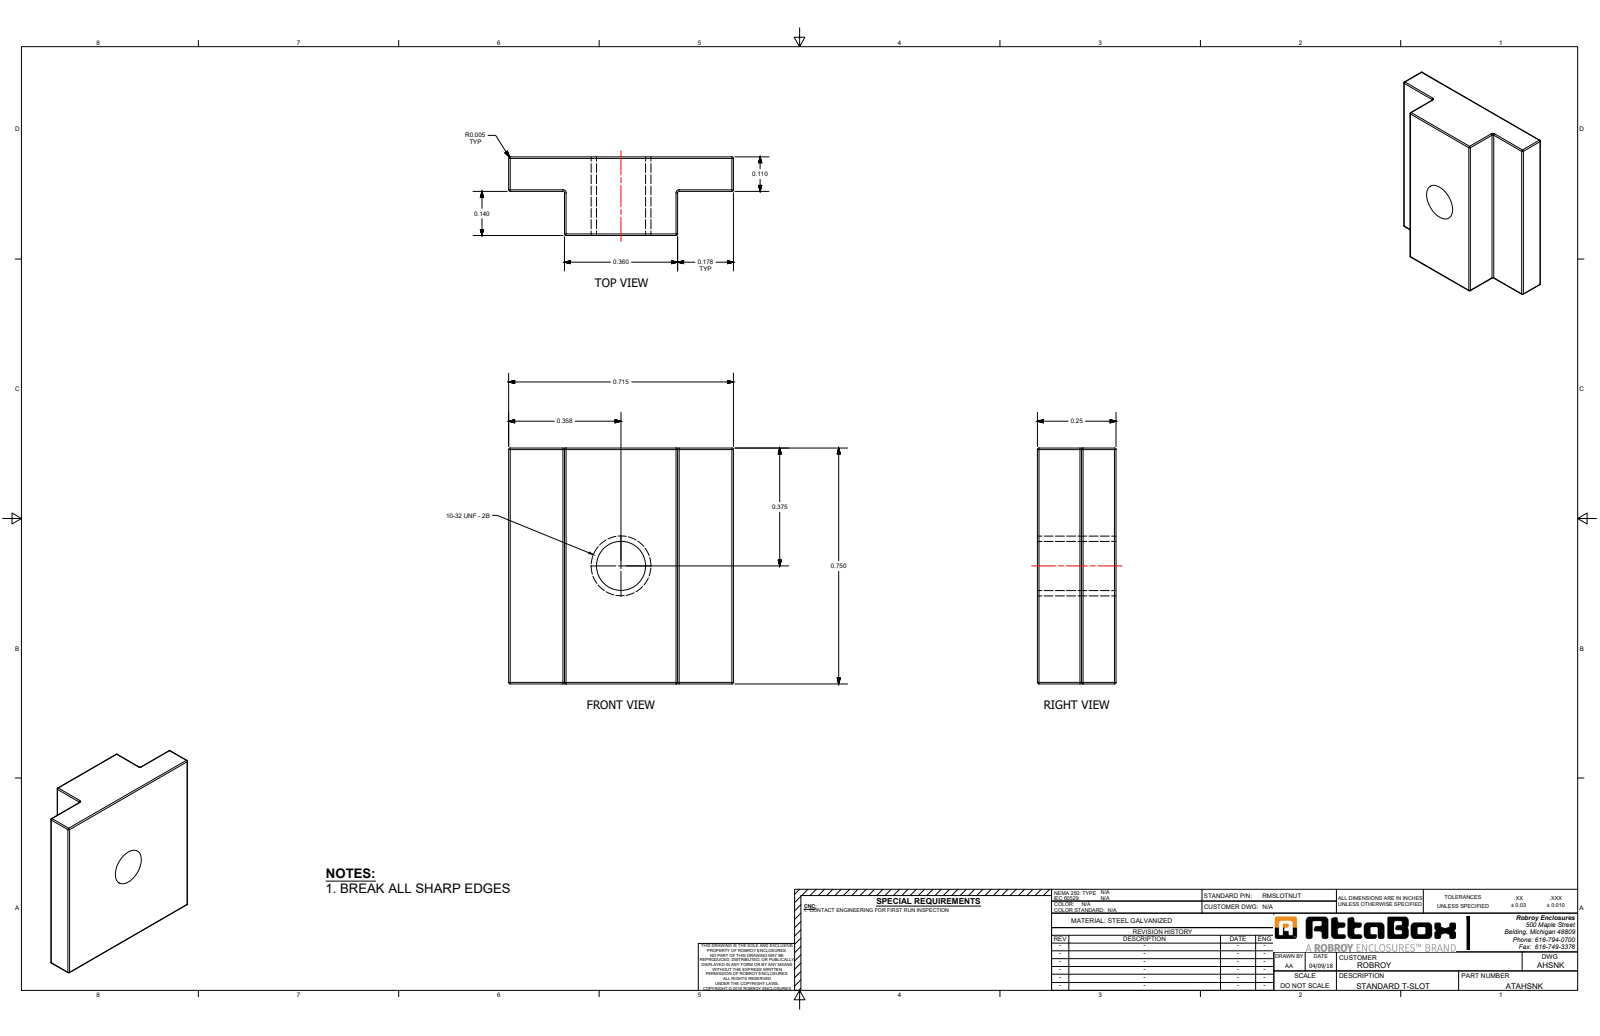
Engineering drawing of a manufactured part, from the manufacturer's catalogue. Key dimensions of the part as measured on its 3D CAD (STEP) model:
Part name (STEP PRODUCT): ATAHSNK
STEP written by: Autodesk Inventor 2018 (AP242_MANAGED_MODEL_BASED_3D_ENGINEERING_MIM_LF)
Units: inches
Bodies: 1 solid, 51 faces (10 planar, 25 cylindrical, 16 other)
Overall size (bounding box): 0.75 × 0.715 × 0.25
Volume: 0.092 in³ · Surface area: 1.767 in²
Round holes (diameter × count): ⌀0.152 ×1
Partial cylindrical surfaces — rounded edges, fillets, slot ends (radius × count): R0.005 ×22
Main face-to-face distances: 0.11, 0.25, 0.14, 0.178, 0.537, 0.75, 0.36, 0.715
